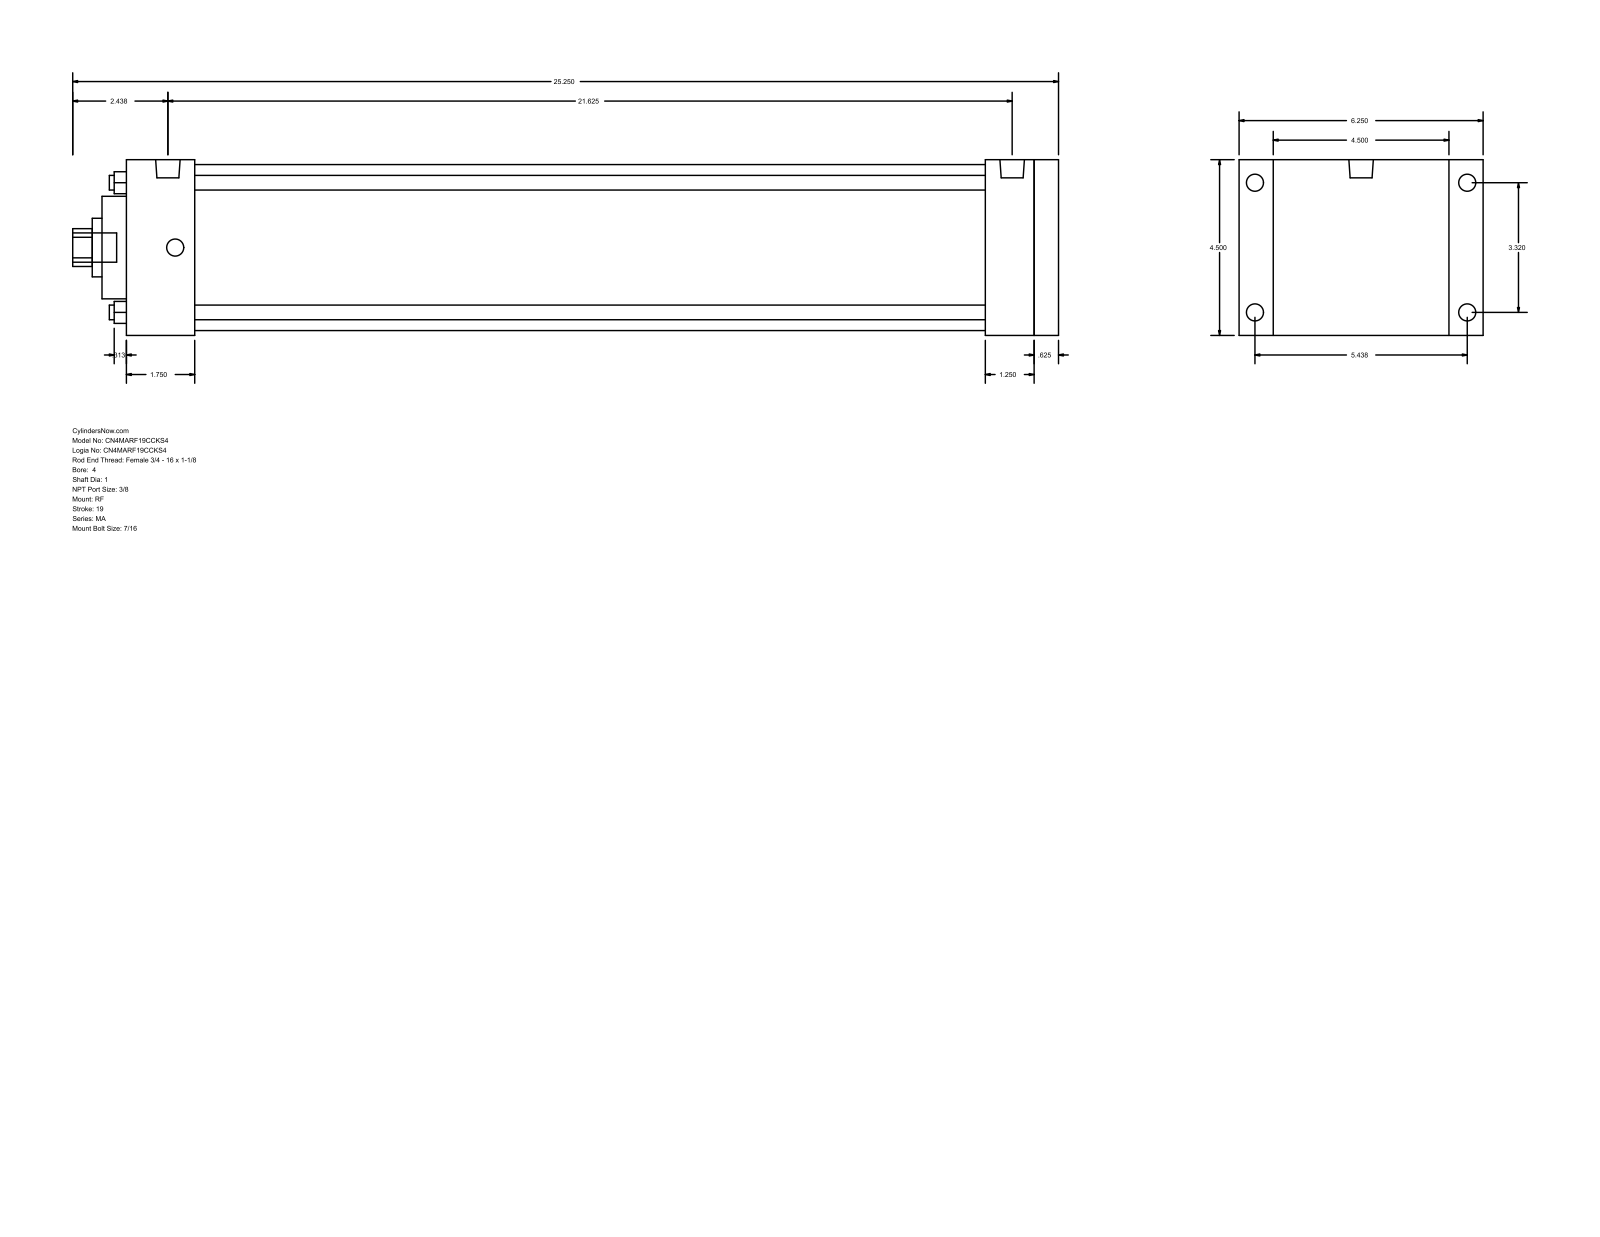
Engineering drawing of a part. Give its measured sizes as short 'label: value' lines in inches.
name: MA_RF__0400_1
written by: GSSL Pune (CONFIG_CONTROL_DESIGN)
unit: in
bodies: 0 solids, 94 faces (65 planar, 29 cylindrical, 0 other)
size: 25.25 × 6.25 × 4.5
holes: 4× ⌀0.375, 1× ⌀1, 1× ⌀1.5, 1× ⌀2.625, 1× ⌀4.25
bosses: 8× ⌀0.437, 2× ⌀0.627, 1× ⌀0.75
rounds: 1× R0.484
face distances: 4.5, 23.875, 0.625, 23.25, 0.875, 5.375, 22, 1.25, 1.875, 1.75
hole spacings: 2.347, 3.32, 4.695
